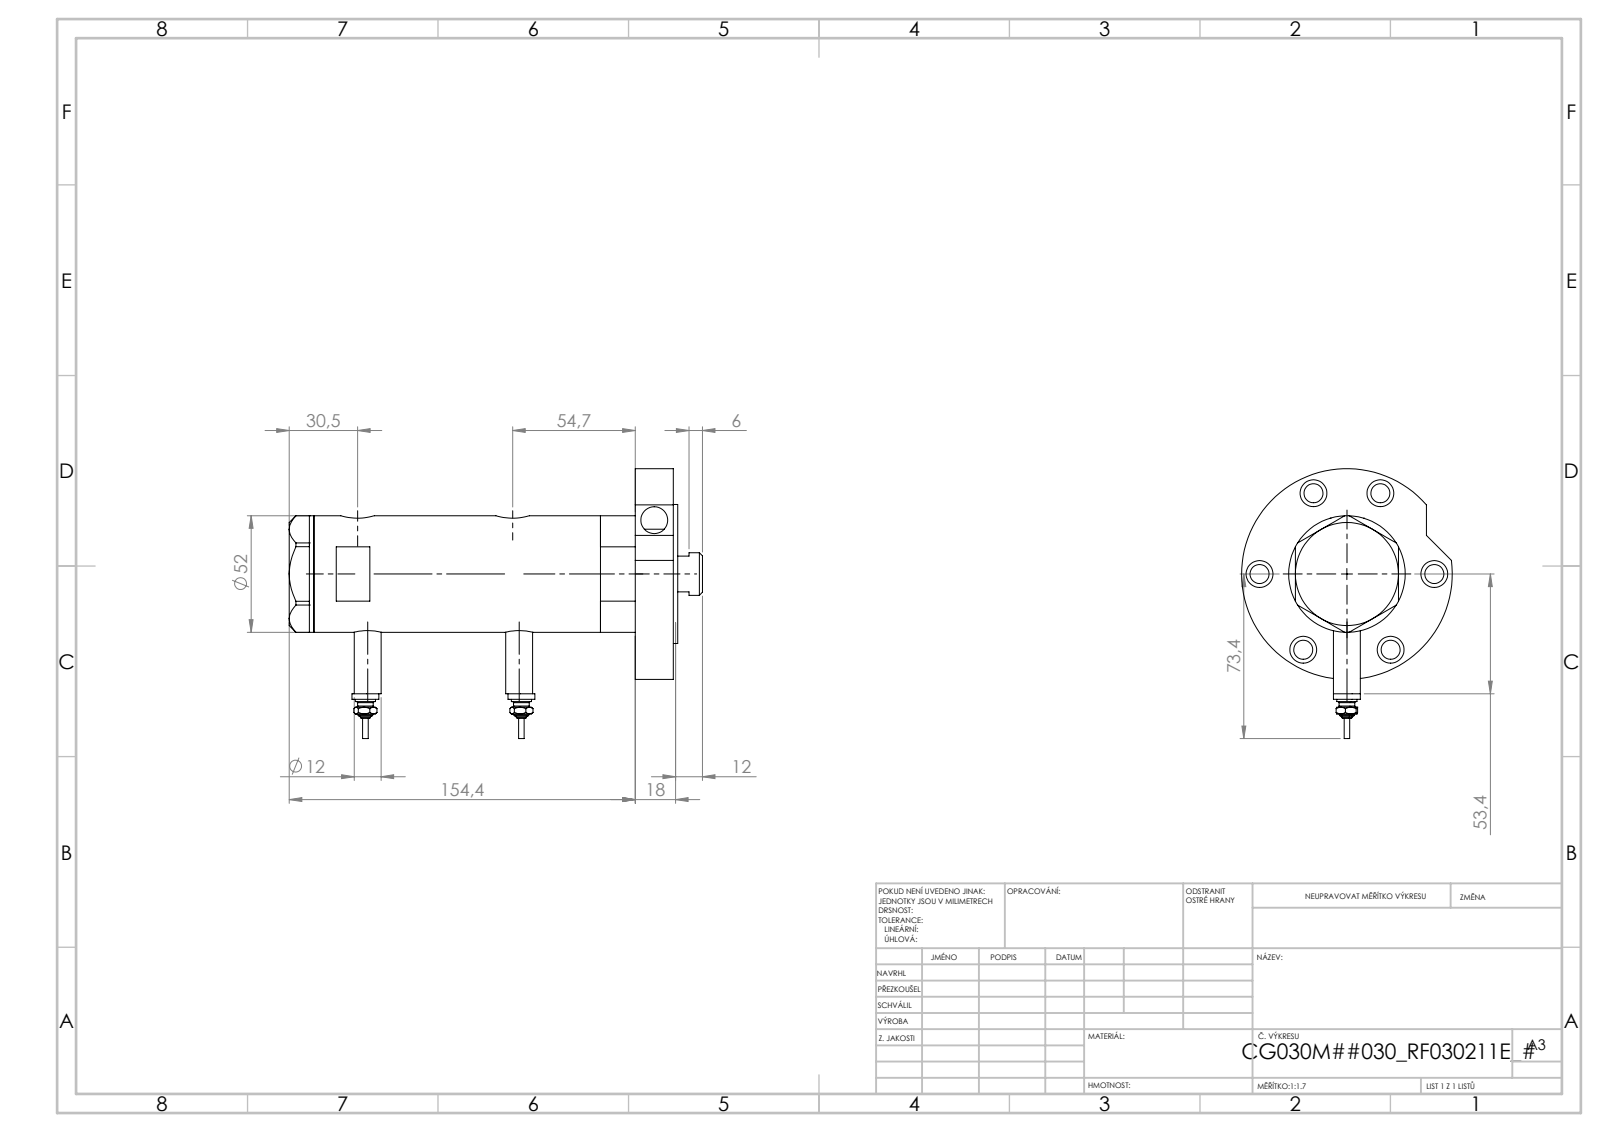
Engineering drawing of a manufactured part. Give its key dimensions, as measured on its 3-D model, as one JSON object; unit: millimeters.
{"part_name": "V270CG_BACK; V270CG_RF211E; V270CG_VC; V270CG_FRONT (+2 more)", "step_written_by": "SolidWorks 2019 (CONFIG_CONTROL_DESIGN)", "units": "millimeters", "bodies": {"solids": 7, "faces": 290, "planar": 106, "cylindrical": 110, "other": 74}, "overall_size": [179.02, 105.3, 94], "volume_mm3": 404117, "surface_area_mm2": 100431, "round_holes": [[12, 7], [8.5, 6], [5, 2], [9.73, 2], [12.5, 2], [15, 2], [6.5, 1], [20, 1], [21.5, 1], [30, 1], [33, 1], [40, 1]], "round_bosses_or_shafts": [[12, 3], [9, 2], [7, 2], [4.34, 2], [2.4, 2], [94, 1], [62, 1], [52, 1]], "face_to_face_distances": [17, 135.45, 152.45, 2, 154.45, 19, 23.81, 111.64, 128.64, 130.64], "hole_center_spacings": [39, 2.9, 4.5, 43.34, 56.75, 59.65, 61.25, 64.15]}
